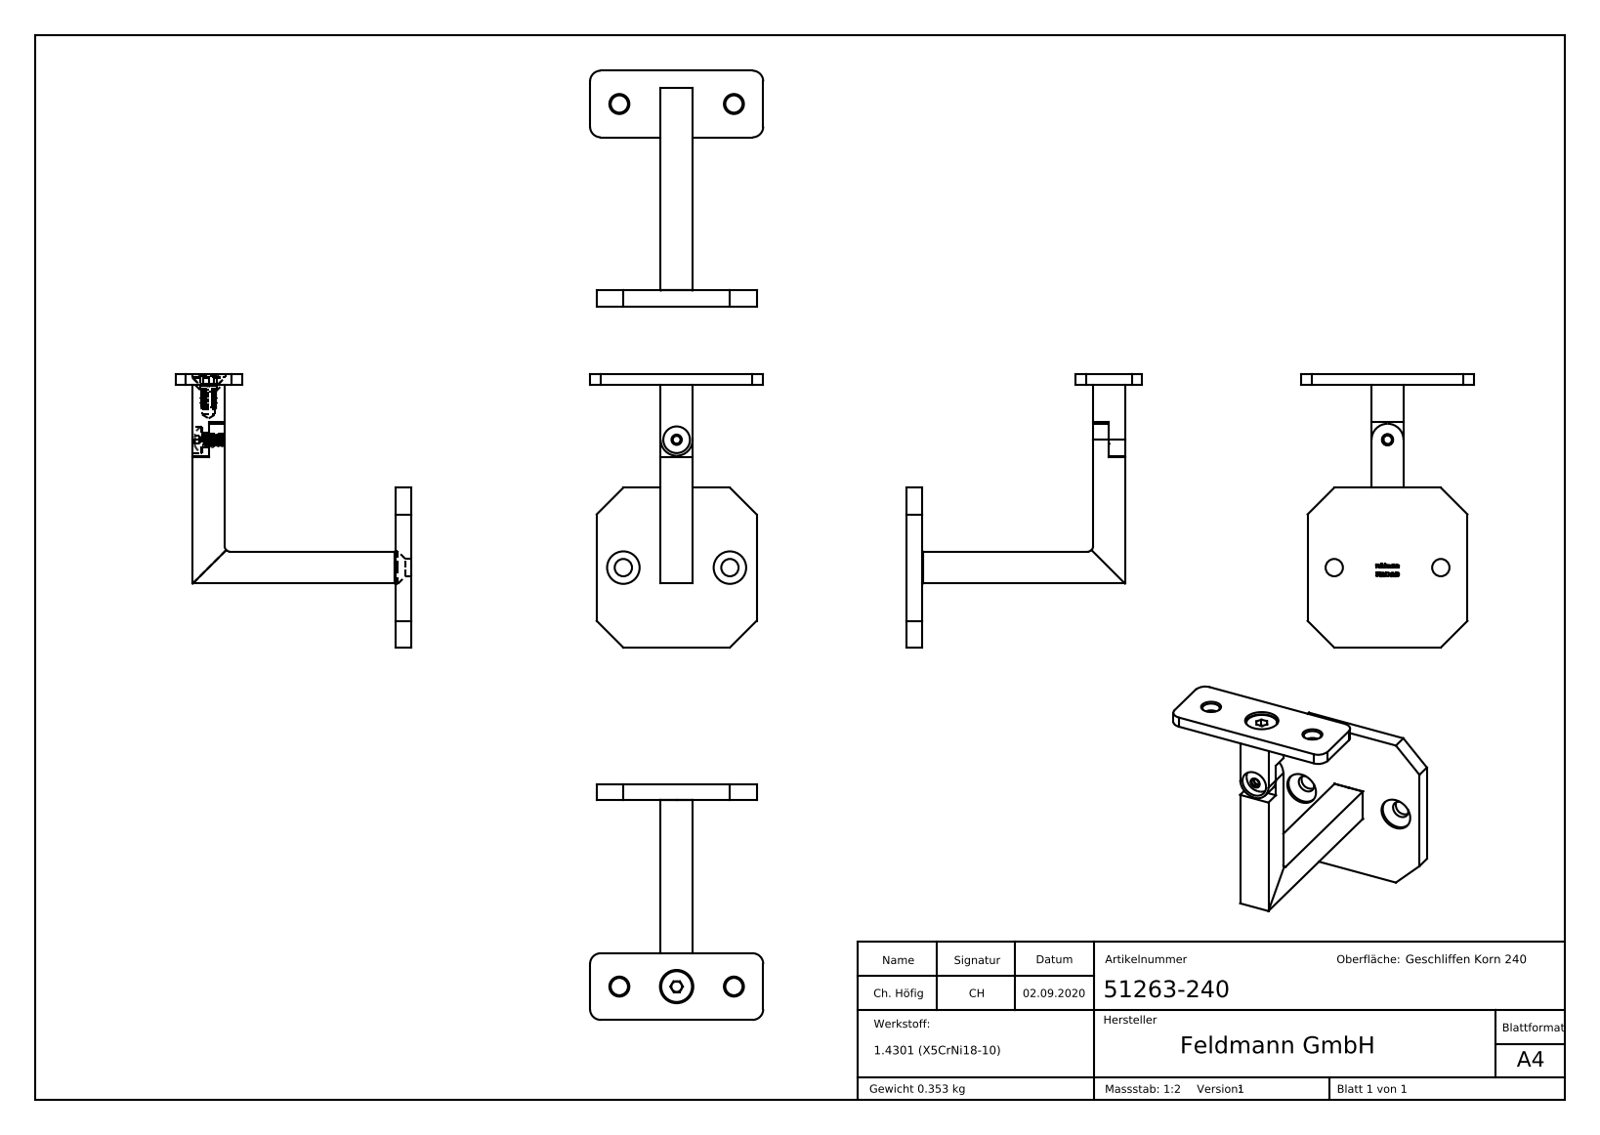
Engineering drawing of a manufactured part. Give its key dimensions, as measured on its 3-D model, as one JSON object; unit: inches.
{"part_name": "5126X-XXX Teil3_51263-240 Teil3; DIN 7380 M5x8; DIN 7380 M5x8_M5x8; socket countersunk head screw_din_DIN 7991 - M6 x 12 --- 12S (+7 more)", "step_written_by": "SolidWorks 2018 (CONFIG_CONTROL_DESIGN)", "units": "inches", "bodies": {"solids": 5, "faces": 441, "planar": 187, "cylindrical": 76, "other": 178}, "overall_size": [4.035, 3.484, 2.559], "volume_in3": 2.748, "surface_area_in2": 31.63, "round_holes": [[0.256, 4], [0.48, 2], [0.165, 1], [0.197, 1], [0.217, 1], [0.276, 1], [0.394, 1], [0.492, 1]], "round_bosses_or_shafts": [[0.472, 1], [0.456, 1], [0.236, 1], [0.158, 1]], "partial_cylinders_radius": [[0.157, 4], [0.079, 1]], "face_to_face_distances": [0.236, 0.472, 0.157, 3.091, 2.992, 0.945, 1.417, 2.756, 2.933, 2.461], "hole_center_spacings": [0.846, 2.047, 1.575, 1.693]}
